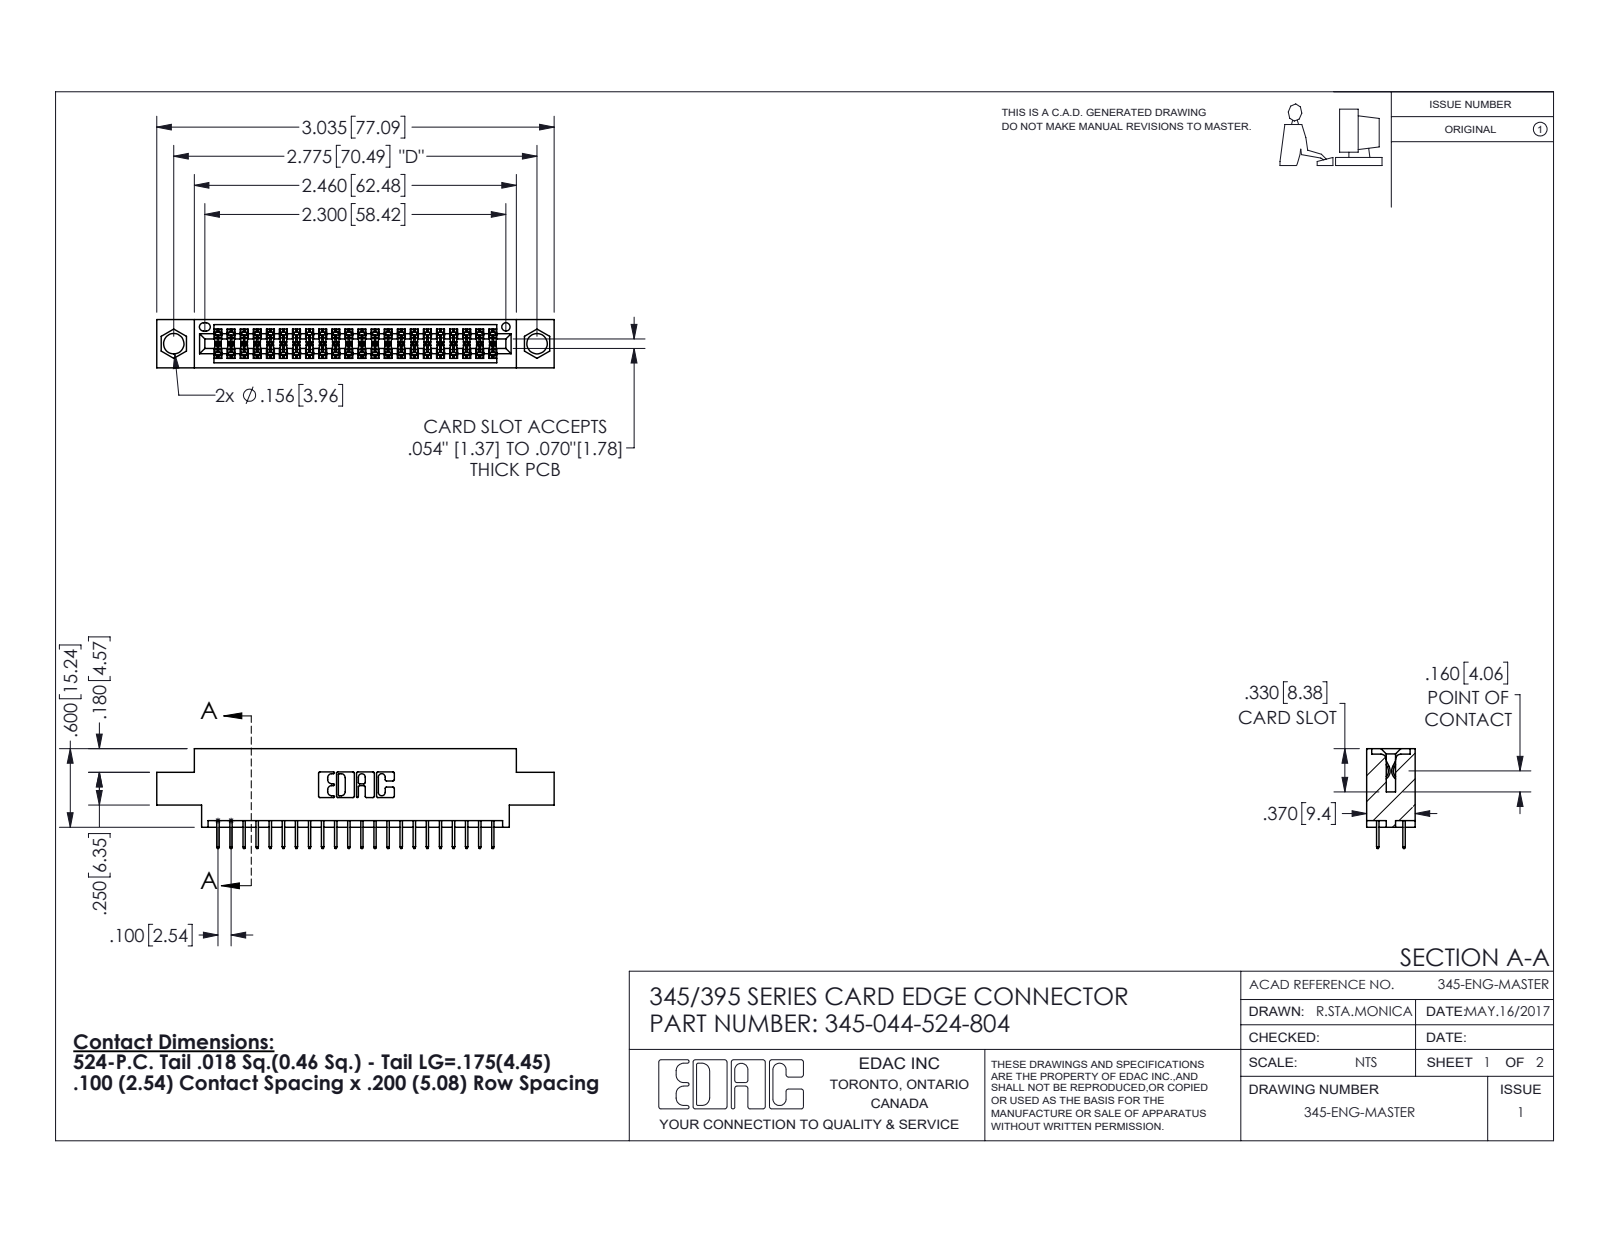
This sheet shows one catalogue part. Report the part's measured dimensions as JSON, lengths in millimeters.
{"part_name": "345-044-524-804; 345 Part_0.170 Offset - 0.156 Dia-TI; 345-292-001_345-293-124", "step_written_by": "SolidWorks 2020 (CONFIG_CONTROL_DESIGN)", "units": "millimeters", "bodies": {"solids": 45, "faces": 2520, "planar": 1814, "cylindrical": 706, "other": 0}, "overall_size": [77.1, 19.4, 9.4], "volume_mm3": 7010, "surface_area_mm2": 9806, "round_holes": [[4, 2], [1.6, 1]], "partial_cylinders_radius": [[0.2, 66], [0.3, 22], [0.2, 6], [0.8, 6], [0.7, 3], [0.4, 2], [0.5, 2], [0.6, 2]], "face_to_face_distances": [1.8, 7.6, 9.4, 5.1, 2.5, 6.9, 0.6, 5.7, 4.4, 1.8], "hole_center_spacings": [6.9, 64.5, 70.5]}
